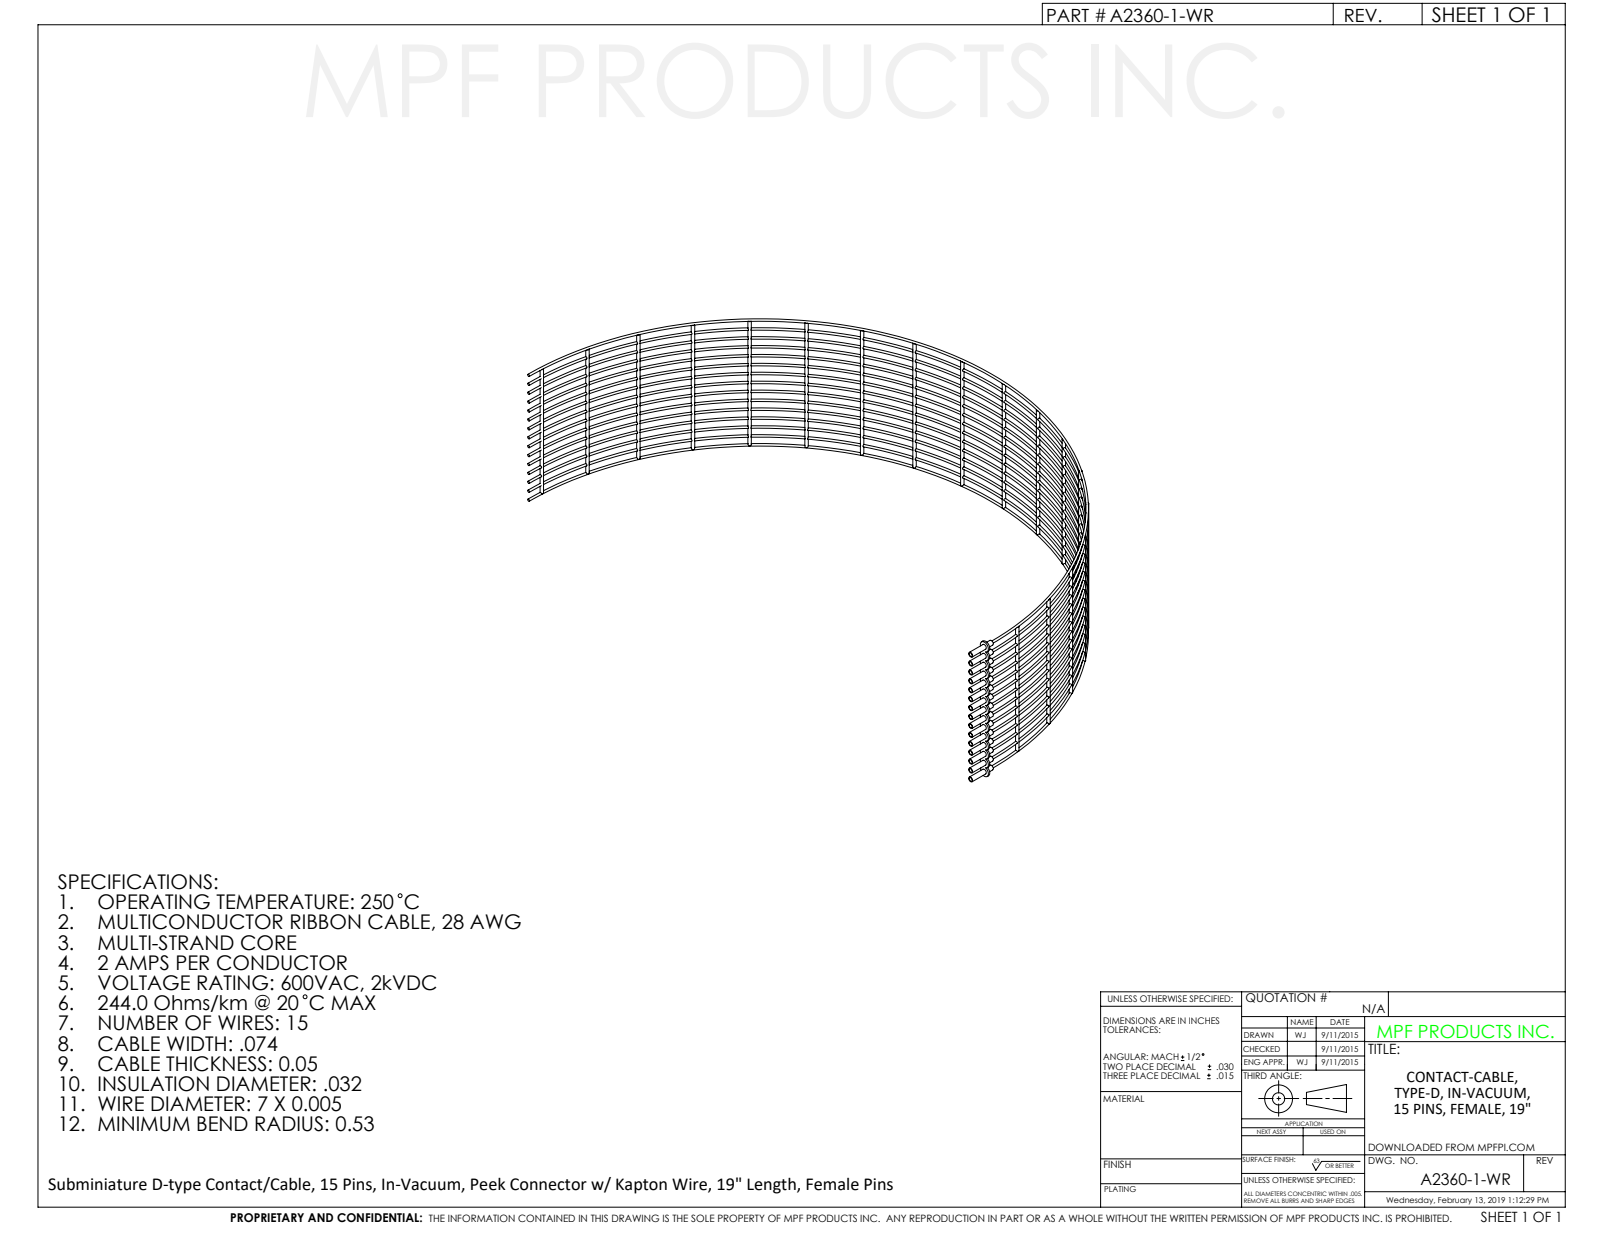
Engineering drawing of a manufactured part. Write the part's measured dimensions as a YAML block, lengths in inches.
part_name: "A2360-1-WR"
step_written_by: "SolidWorks 2012 (CONFIG_CONTROL_DESIGN)"
units: inches
bodies: {solids: 1, faces: 851, planar: 135, cylindrical: 170, other: 546}
overall_size: [6.064, 3.28, 1.505]
volume: 0.083
surface_area: 13.12
round_holes:
  - {diameter: 0.038, count: 15}
round_bosses_or_shafts:
  - {diameter: 0.032, count: 18}
  - {diameter: 0.05, count: 15}
  - {diameter: 0.105, count: 14}
partial_cylinders:
  - {radius: 0.053, count: 1}
face_to_face_distances: [0.018, 0.074, 0.091, 0.159, 0.086, 0.068, 0.269, 0.195, 0.177, 0.109]
hole_center_spacings: [0.1, 0.2, 0.3, 0.4, 0.5, 0.6, 0.7, 0.8]
